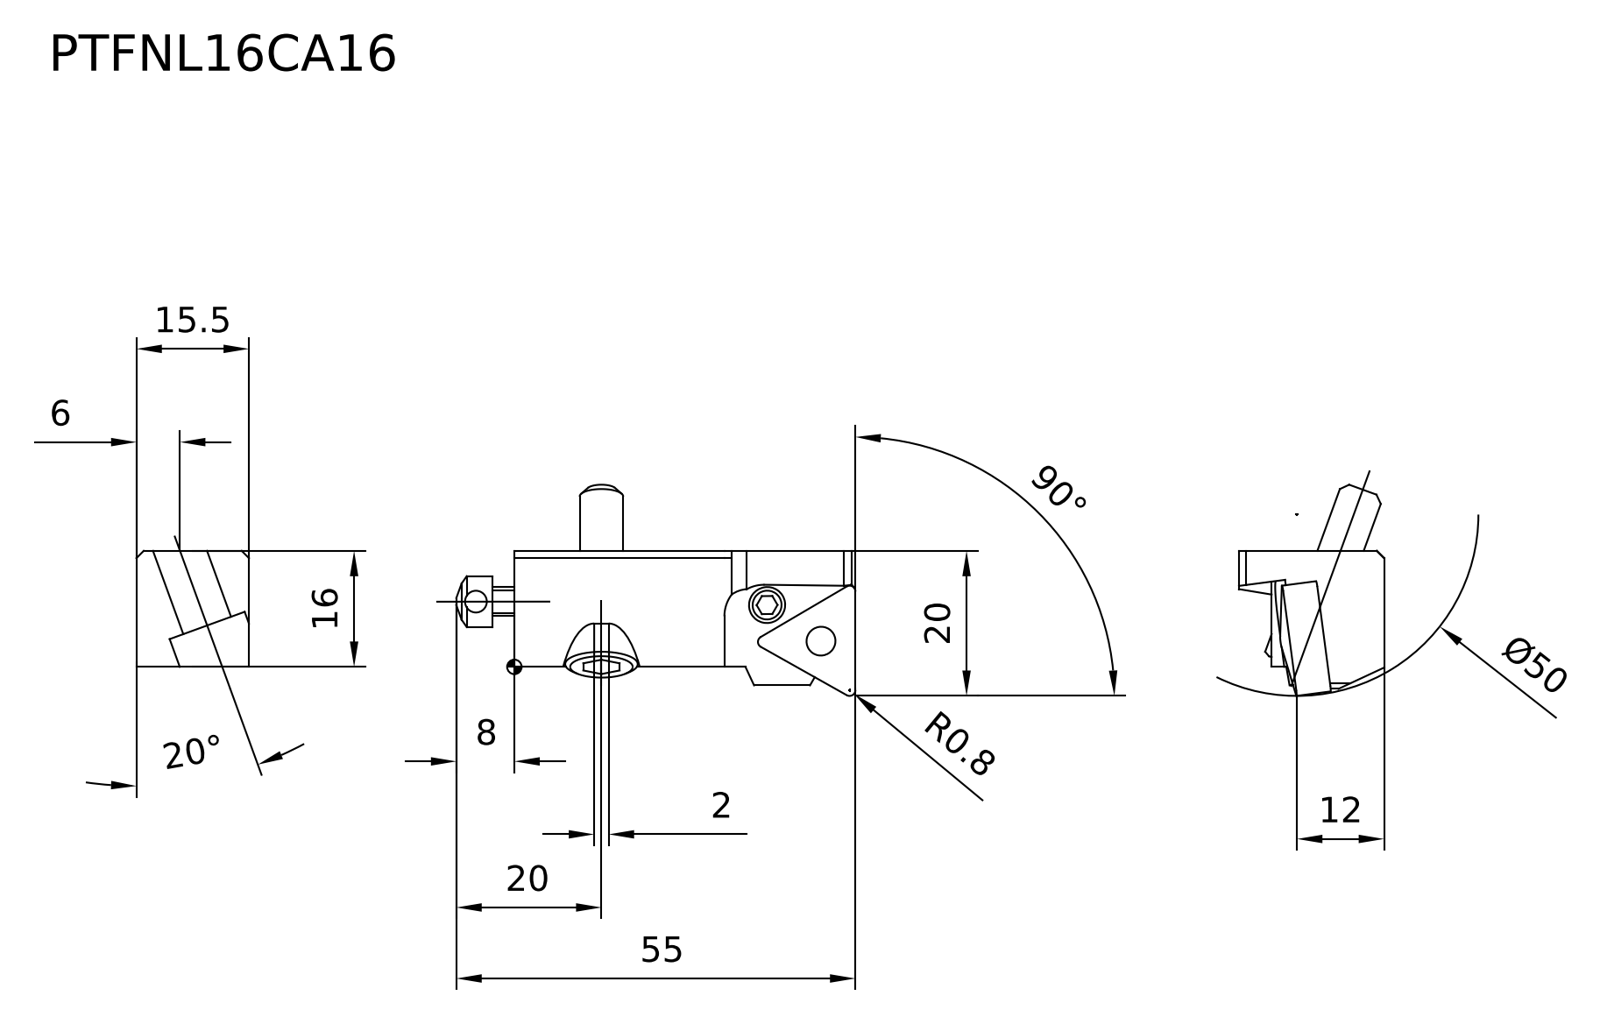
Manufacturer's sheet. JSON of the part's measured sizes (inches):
{"part_name": "PTFNL16CA16_ASM", "step_written_by": "SIEMENS PLM Software NX 10.0 (AUTOMOTIVE_DESIGN)", "units": "inches", "bodies": {"solids": 8, "faces": 234, "planar": 107, "cylindrical": 64, "other": 63}, "overall_size": [2.461, 1.344, 1.275], "volume_in3": 1.007, "surface_area_in2": 13.26, "round_holes": [[0.142, 2], [0.197, 2], [0.098, 1], [0.165, 1], [0.189, 1]], "round_bosses_or_shafts": [[0.236, 2], [0.541, 1], [0.394, 1], [0.315, 1], [0.197, 1], [0.189, 1], [0.177, 1], [0.114, 1]], "partial_cylinders_radius": [[0.012, 4], [0.02, 2], [0.177, 2], [0.197, 2], [0.016, 1], [0.031, 1], [0.047, 1], [0.067, 1]], "face_to_face_distances": [2.109, 0.63, 0.669, 0.89, 0.221, 0.293, 0.394, 1.024, 0.125, 0.168], "hole_center_spacings": [0.388, 0.389, 2.049]}
